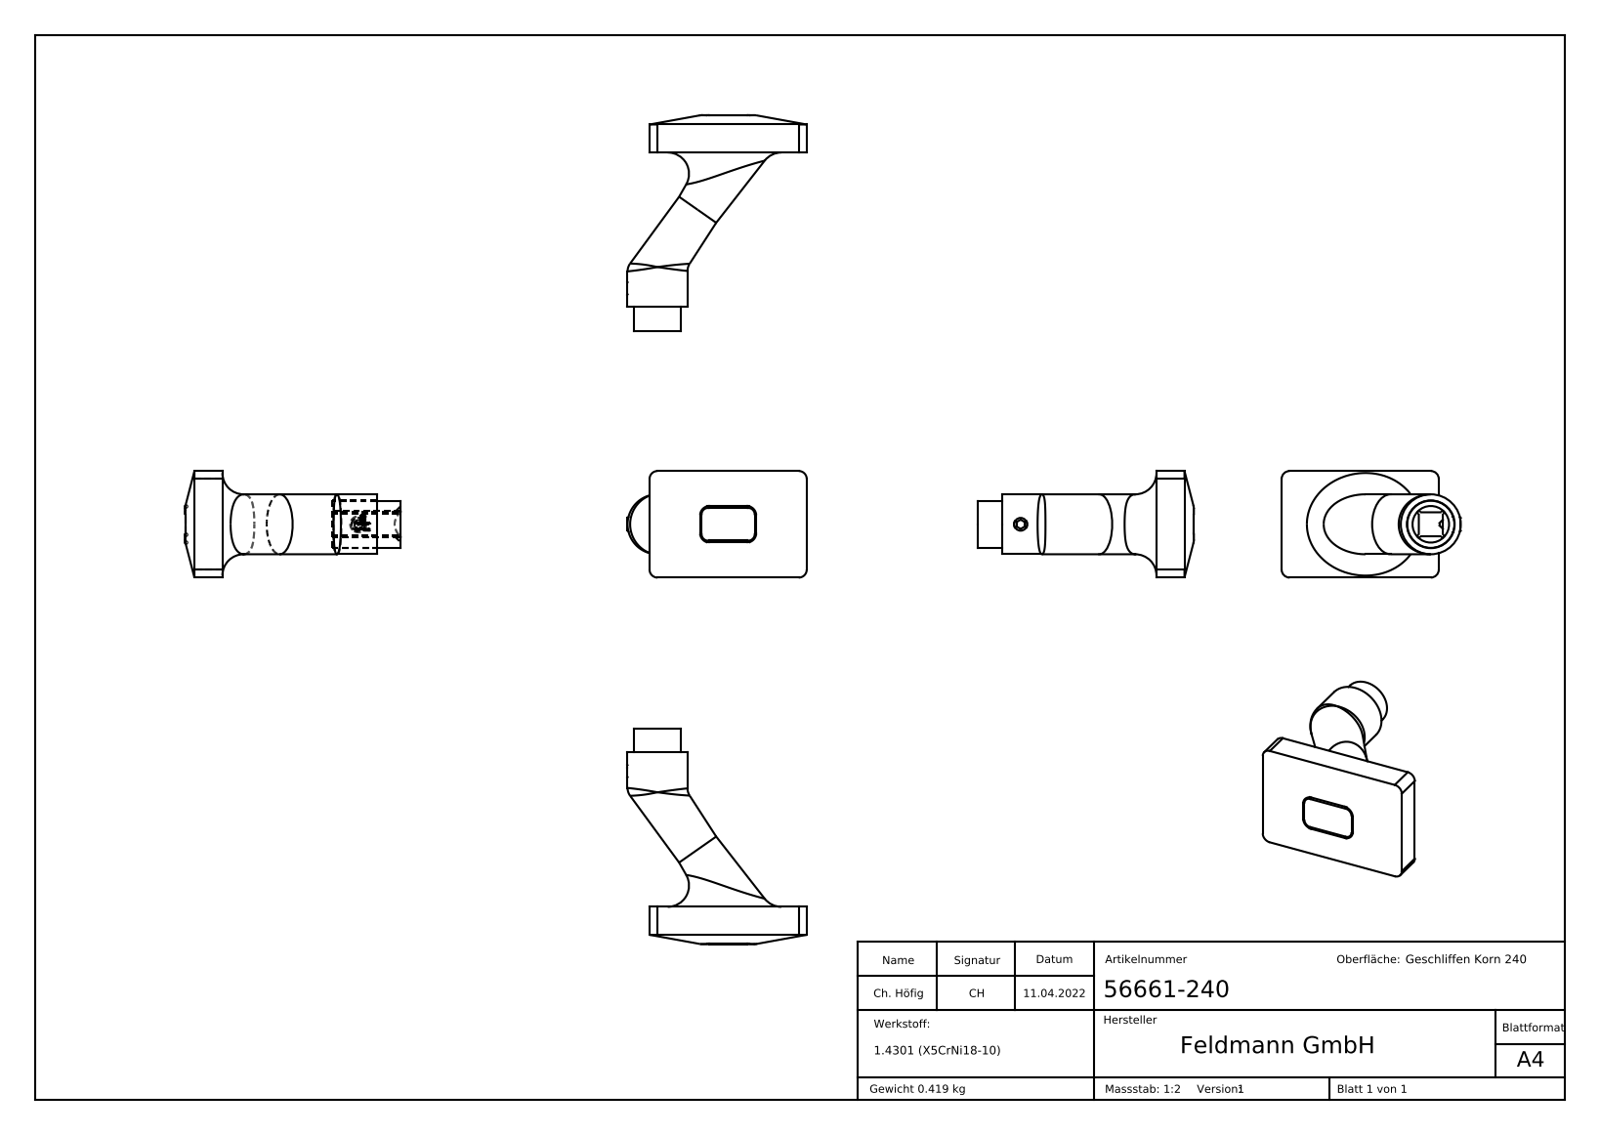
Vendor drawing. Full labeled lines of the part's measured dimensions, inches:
Part name (STEP PRODUCT): 56661-240; DIN914_DIN 914 M6x8; 56661-240 Teil1_56661-240 Teil1
STEP written by: SolidWorks 2018 (CONFIG_CONTROL_DESIGN)
Units: inches
Bodies: 2 solids, 321 faces (169 planar, 14 cylindrical, 138 other)
Overall size (bounding box): 3.189 × 2.648 × 1.575
Volume: 3.22 in³ · Surface area: 22.56 in²
Round holes (diameter × count): ⌀0.197 ×1, ⌀0.705 ×1
Round bosses / shafts (diameter × count): ⌀0.886 ×1, ⌀0.697 ×1, ⌀0.236 ×1
Partial cylindrical surfaces — rounded edges, fillets, slot ends (radius × count): R0.02 ×4, R0.118 ×4
Main face-to-face distances: 1.575, 0.354, 0.61, 0.965, 2.323, 0.551, 0.295, 2.028, 0.059, 2.382
